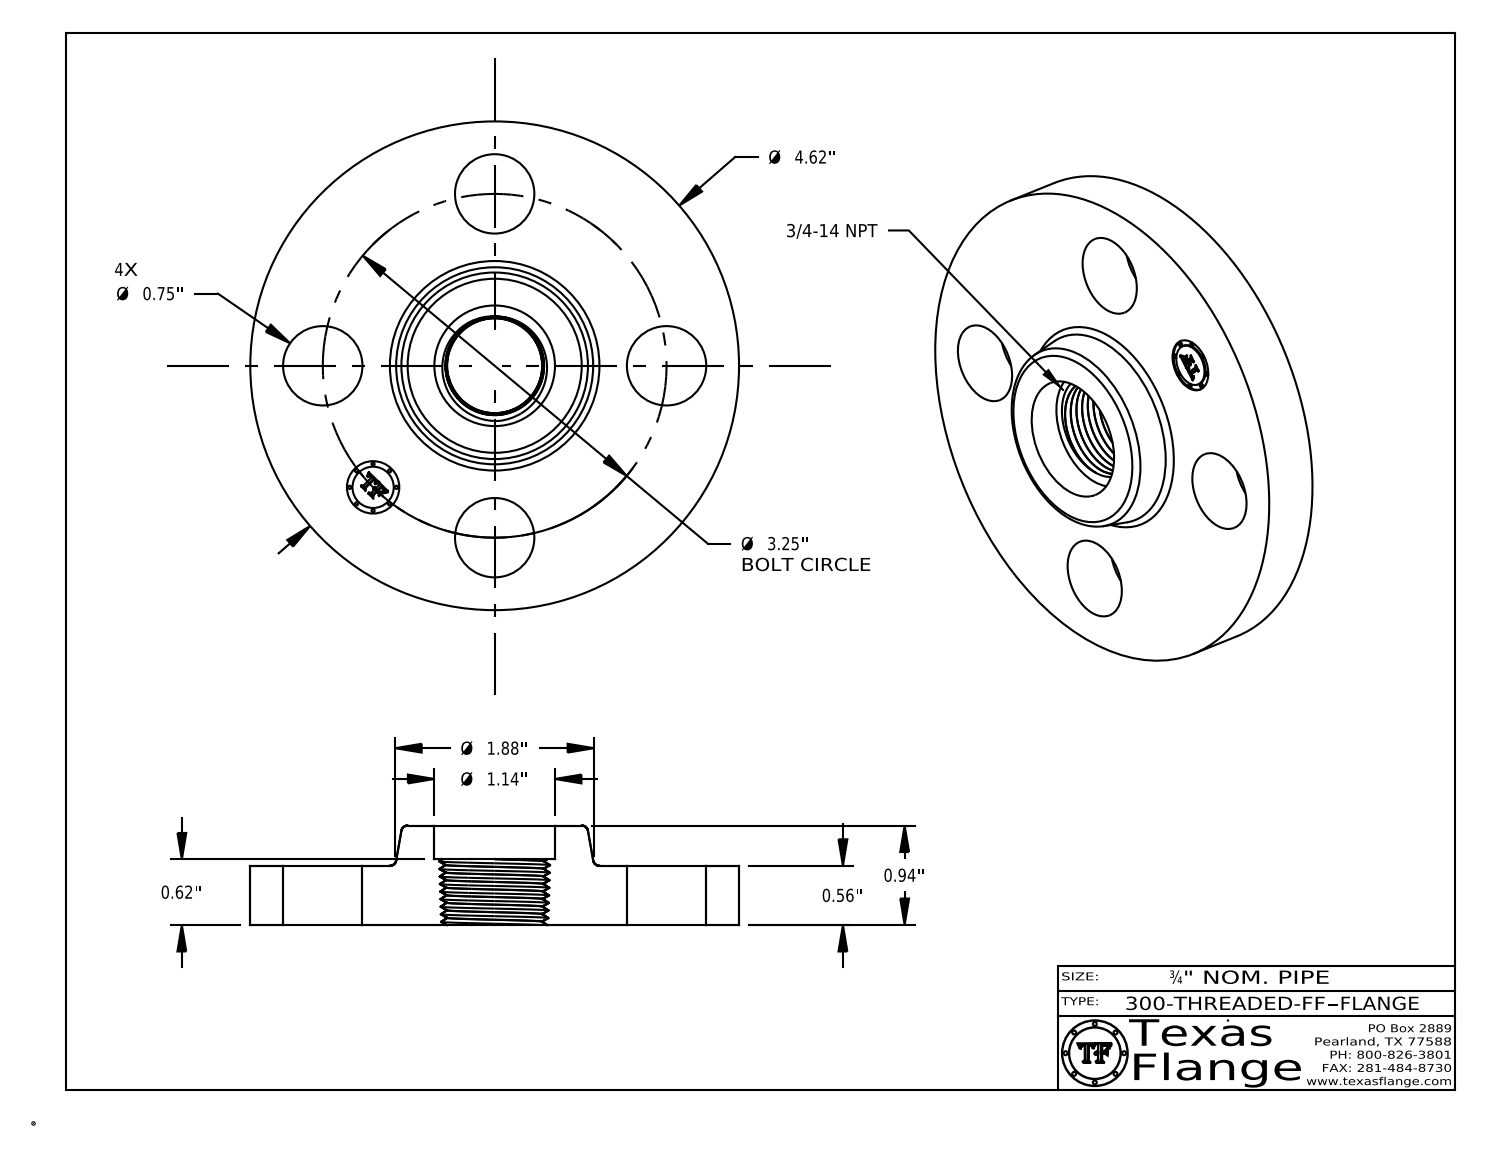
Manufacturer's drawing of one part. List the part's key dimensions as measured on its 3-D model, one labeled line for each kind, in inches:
Part name (STEP PRODUCT): 300-THREADED-FF
STEP written by: CATIA V5 STEP AP214 (AUTOMOTIVE_DESIGN)
Units: inches
Bodies: 1 solid, 500 faces (369 planar, 32 cylindrical, 99 other)
Overall size (bounding box): 4.62 × 4.62 × 0.94
Volume: 8.594 in³ · Surface area: 48.31 in²
Round holes (diameter × count): ⌀0.75 ×4, ⌀0.495 ×1, ⌀1.14 ×1
Round bosses / shafts (diameter × count): ⌀0.03 ×8, ⌀4.62 ×1, ⌀0.39 ×1
Main face-to-face distances: 0.56, 0.94, 0.38, 0.62, 0.06, 0.32, 0.545, 0.015, 0.075, 0.395
Hole centre spacings: 1.625, 2.298, 1.244, 3.003, 3.25
